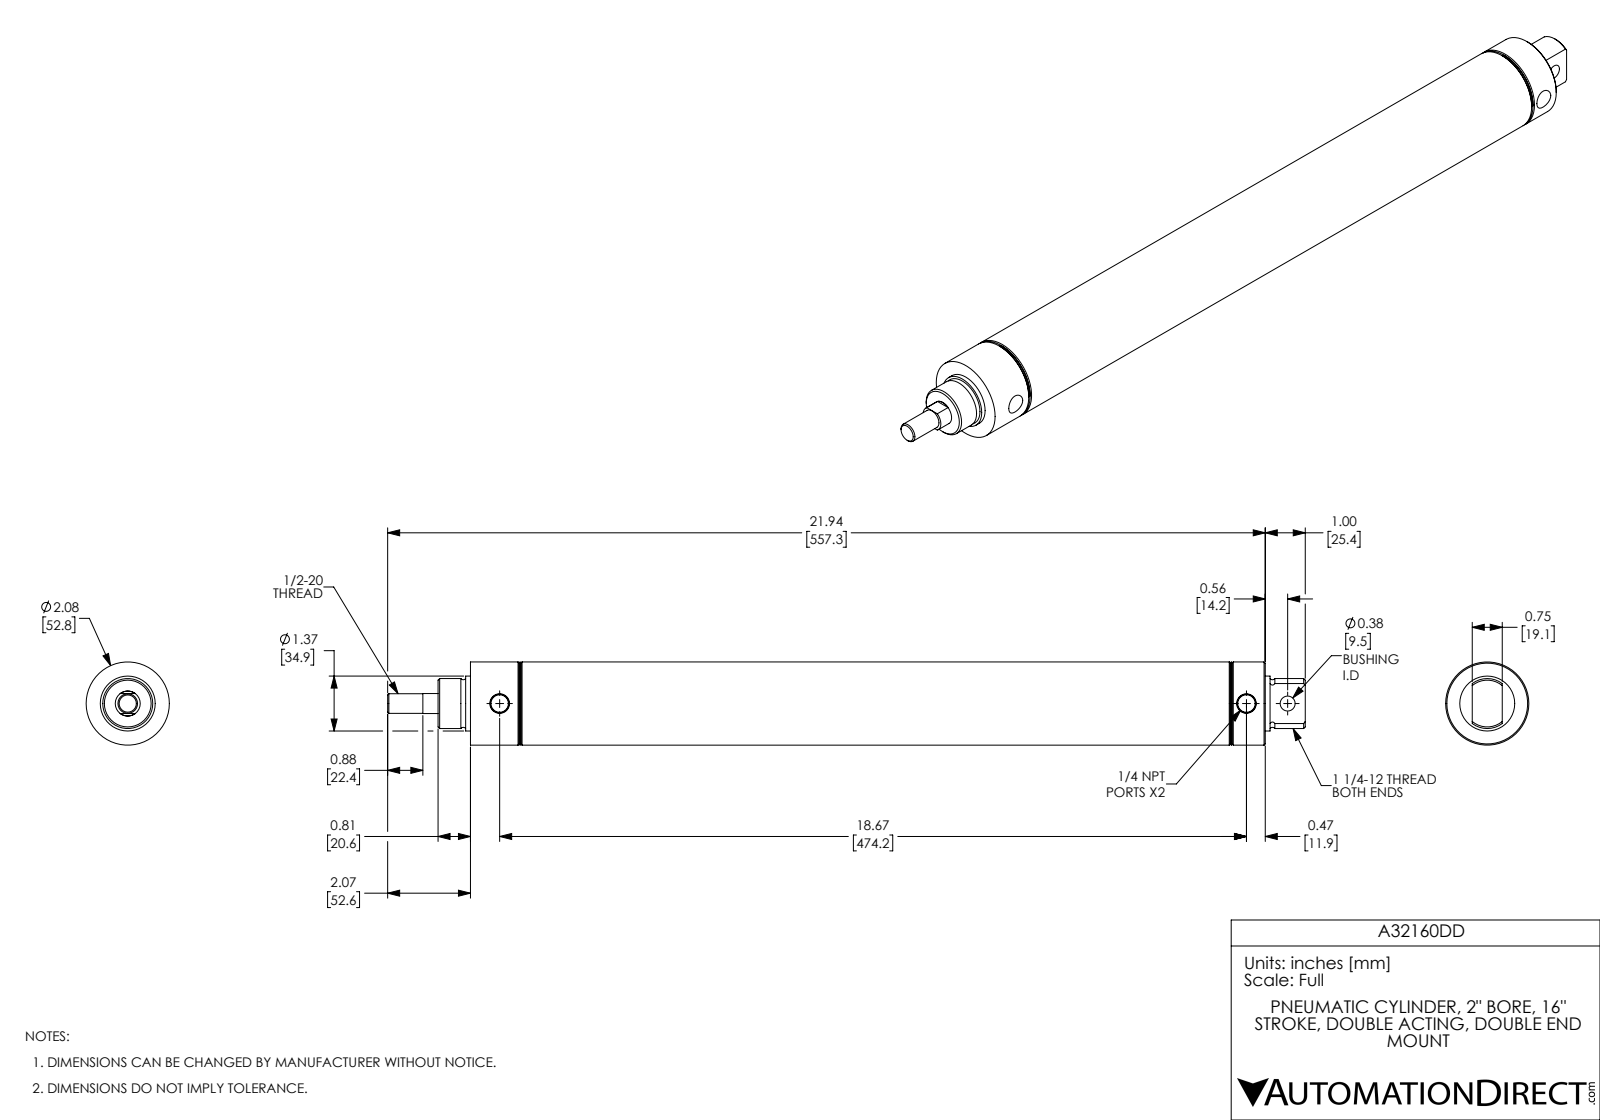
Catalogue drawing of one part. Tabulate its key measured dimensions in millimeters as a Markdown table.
| quantity | value |
| --- | --- |
| part name | A32160DD-MainBody; A32160DD-Rod; A32160DD |
| STEP written by | SolidWorks 2017 (AUTOMOTIVE_DESIGN) |
| units | millimeters |
| bodies | 2 solids, 88 faces (20 planar, 30 cylindrical, 38 other) |
| overall size | 582.7 × 52.8 × 52.8 |
| volume | 393 100 mm³ |
| surface area | 199 200 mm² |
| round holes (diameter × count) | 11.1 × 2, 9.5 × 1, 15.9 × 1, 50.8 × 1 |
| round bosses / shafts (diameter × count) | 52.8 × 1, 34.9 × 1, 31.8 × 1, 12.5 × 1 |
| main face-to-face distances | 12.7, 419.1, 406.4, 461.9, 449.2, 42.8, 42.8, 55.5, 461.9, 504.7 |
| hole center spacings | 26.2, 474.2, 500.4 |
